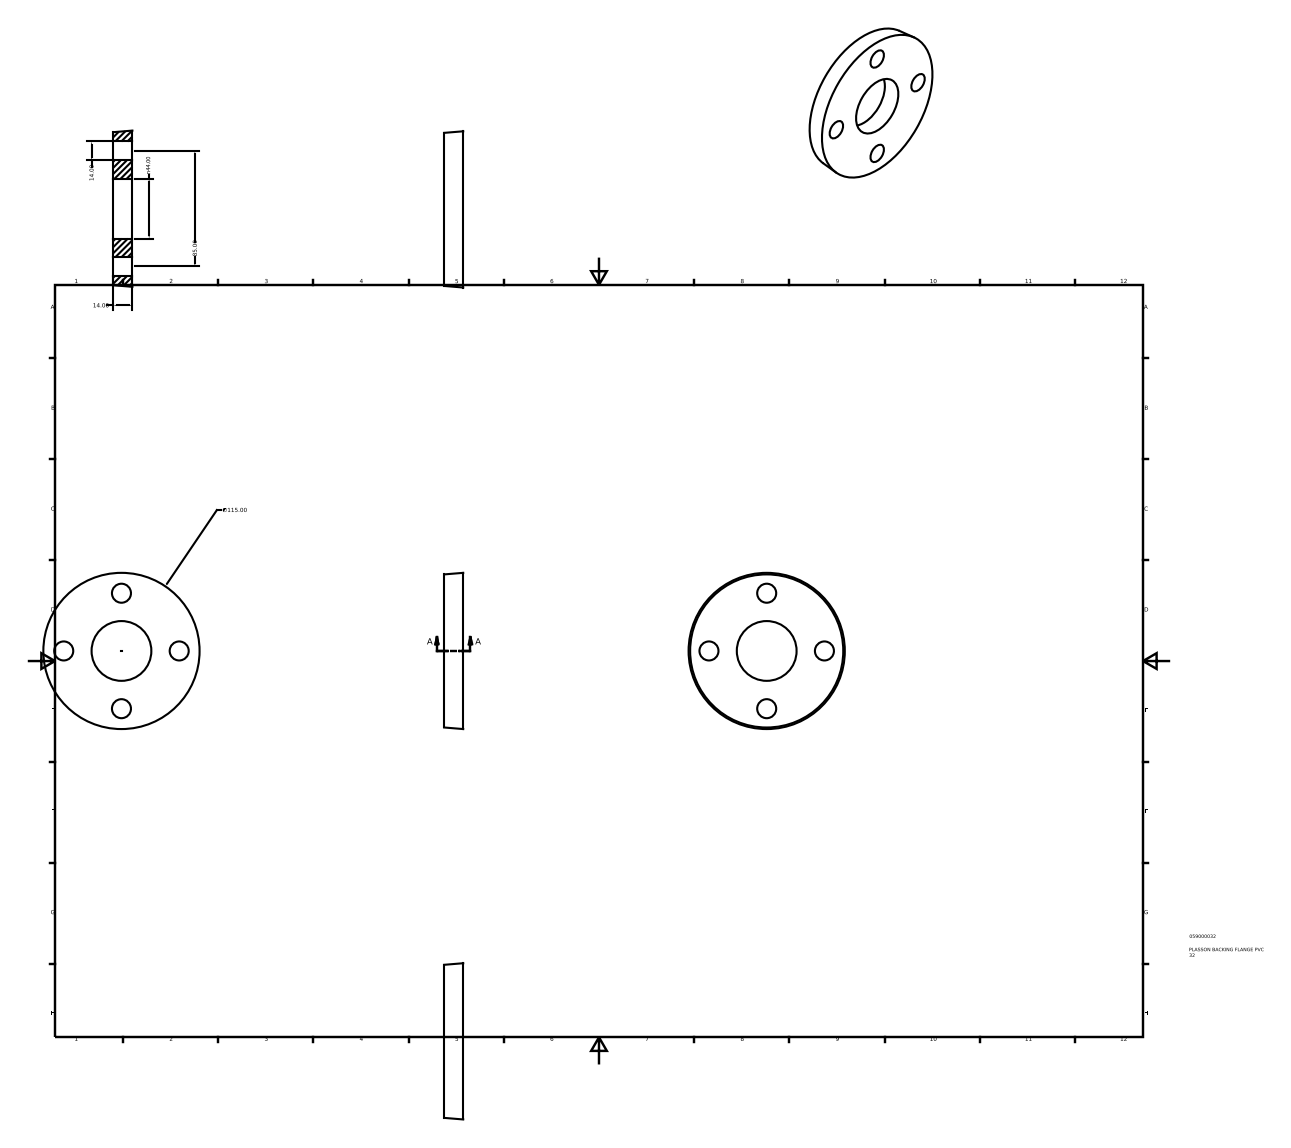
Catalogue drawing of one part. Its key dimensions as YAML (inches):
part_name: "059000032"
step_written_by: "Autodesk Inventor 2015 (AUTOMOTIVE_DESIGN)"
units: inches
bodies: {solids: 1, faces: 8, planar: 2, cylindrical: 5, other: 1}
overall_size: [4.528, 4.528, 0.551]
volume: 6.872
surface_area: 39.54
round_holes:
  - {diameter: 0.551, count: 4}
  - {diameter: 1.732, count: 1}
face_to_face_distances: [0.551]
hole_center_spacings: [1.673, 2.366, 3.346]
